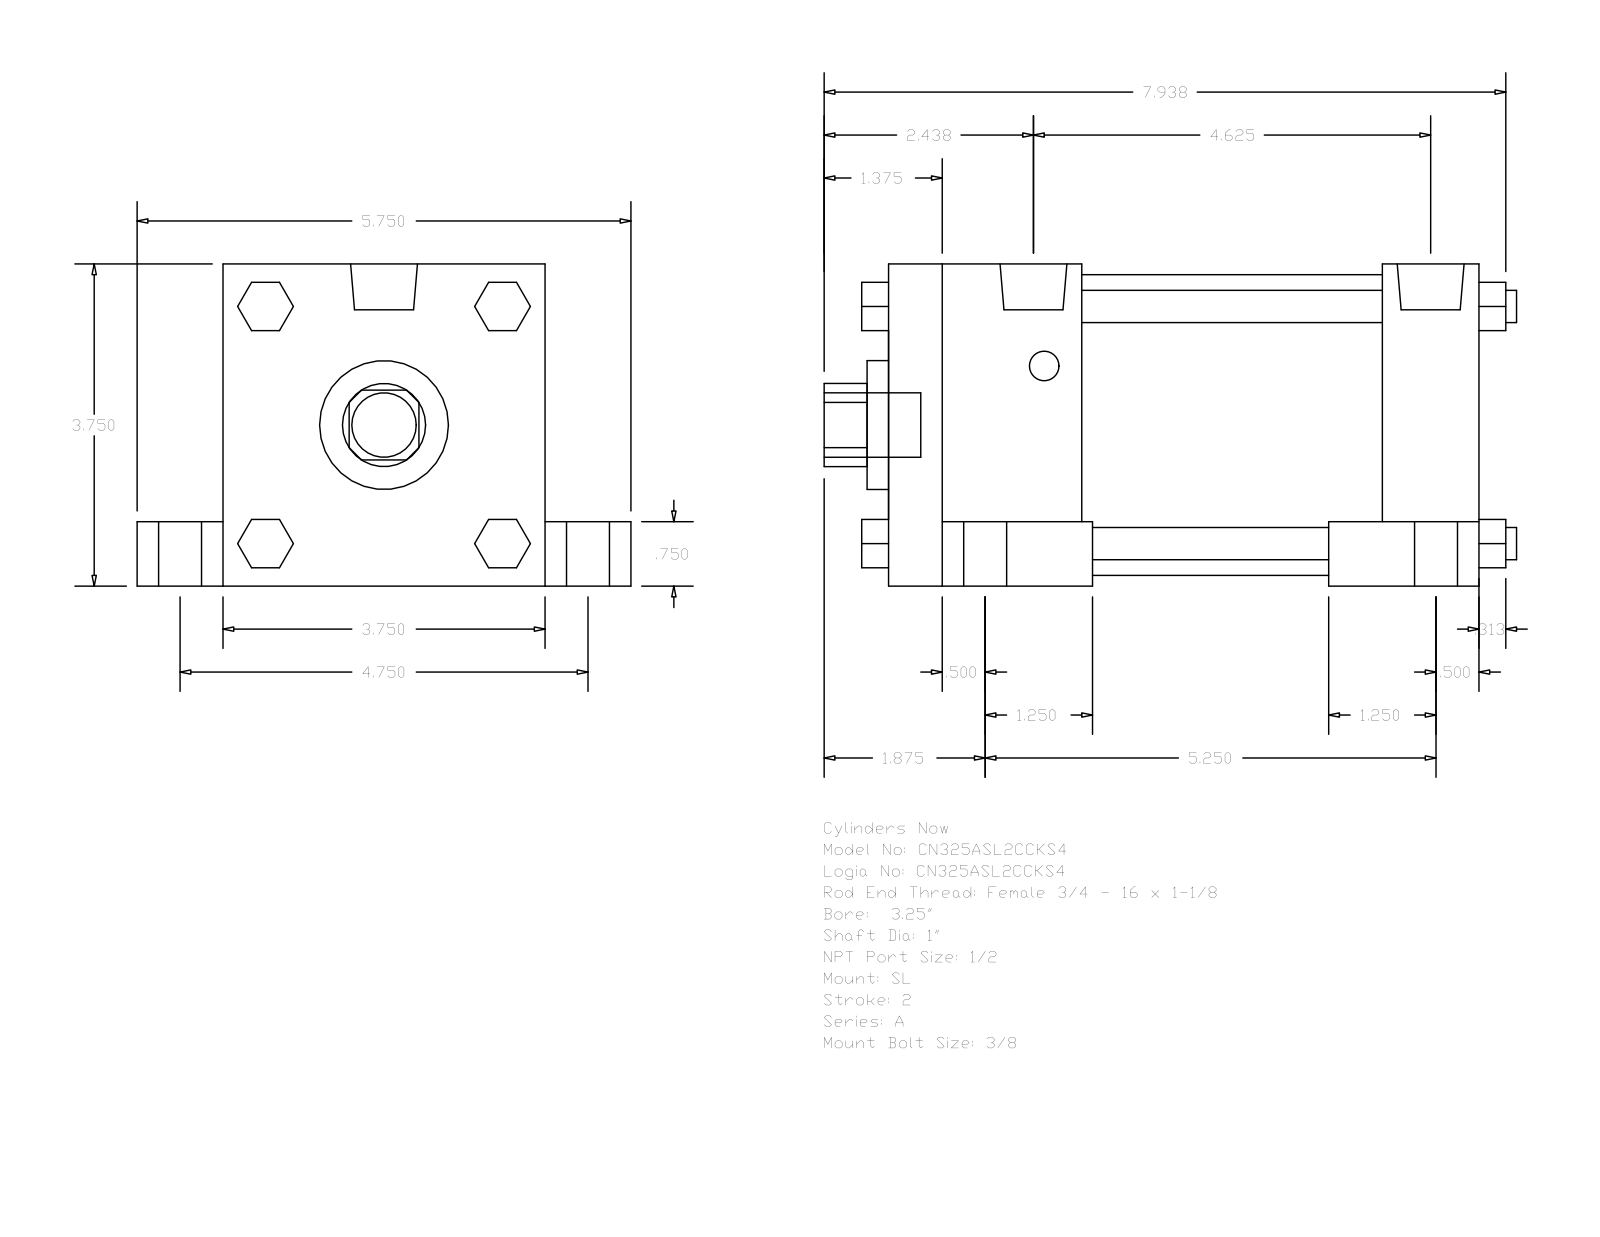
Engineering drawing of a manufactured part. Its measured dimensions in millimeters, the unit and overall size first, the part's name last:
Units: millimetres
Overall size (bounding box): 204.79 × 146.05 × 95.25
Round holes (diameter × count): ⌀25.4 ×1, ⌀38.1 ×1, ⌀88.9 ×1
Round bosses / shafts (diameter × count): ⌀19.05 ×5, ⌀12.7 ×4, ⌀9.53 ×4, ⌀8.73 ×4, ⌀19.77 ×2
Partial cylindrical surfaces — rounded edges, fillets, slot ends (radius × count): R12.29 ×1
Main face-to-face distances: 95.24, 174.63, 120.65, 19.05, 25.41, 76.19, 57.15, 146.05, 88.9, 117.48
Bodies: 0 solids, 150 faces (114 planar, 36 cylindrical, 0 other)
Part name (STEP PRODUCT): A_SL__0325_1
STEP written by: GSSL Pune (CONFIG_CONTROL_DESIGN)
